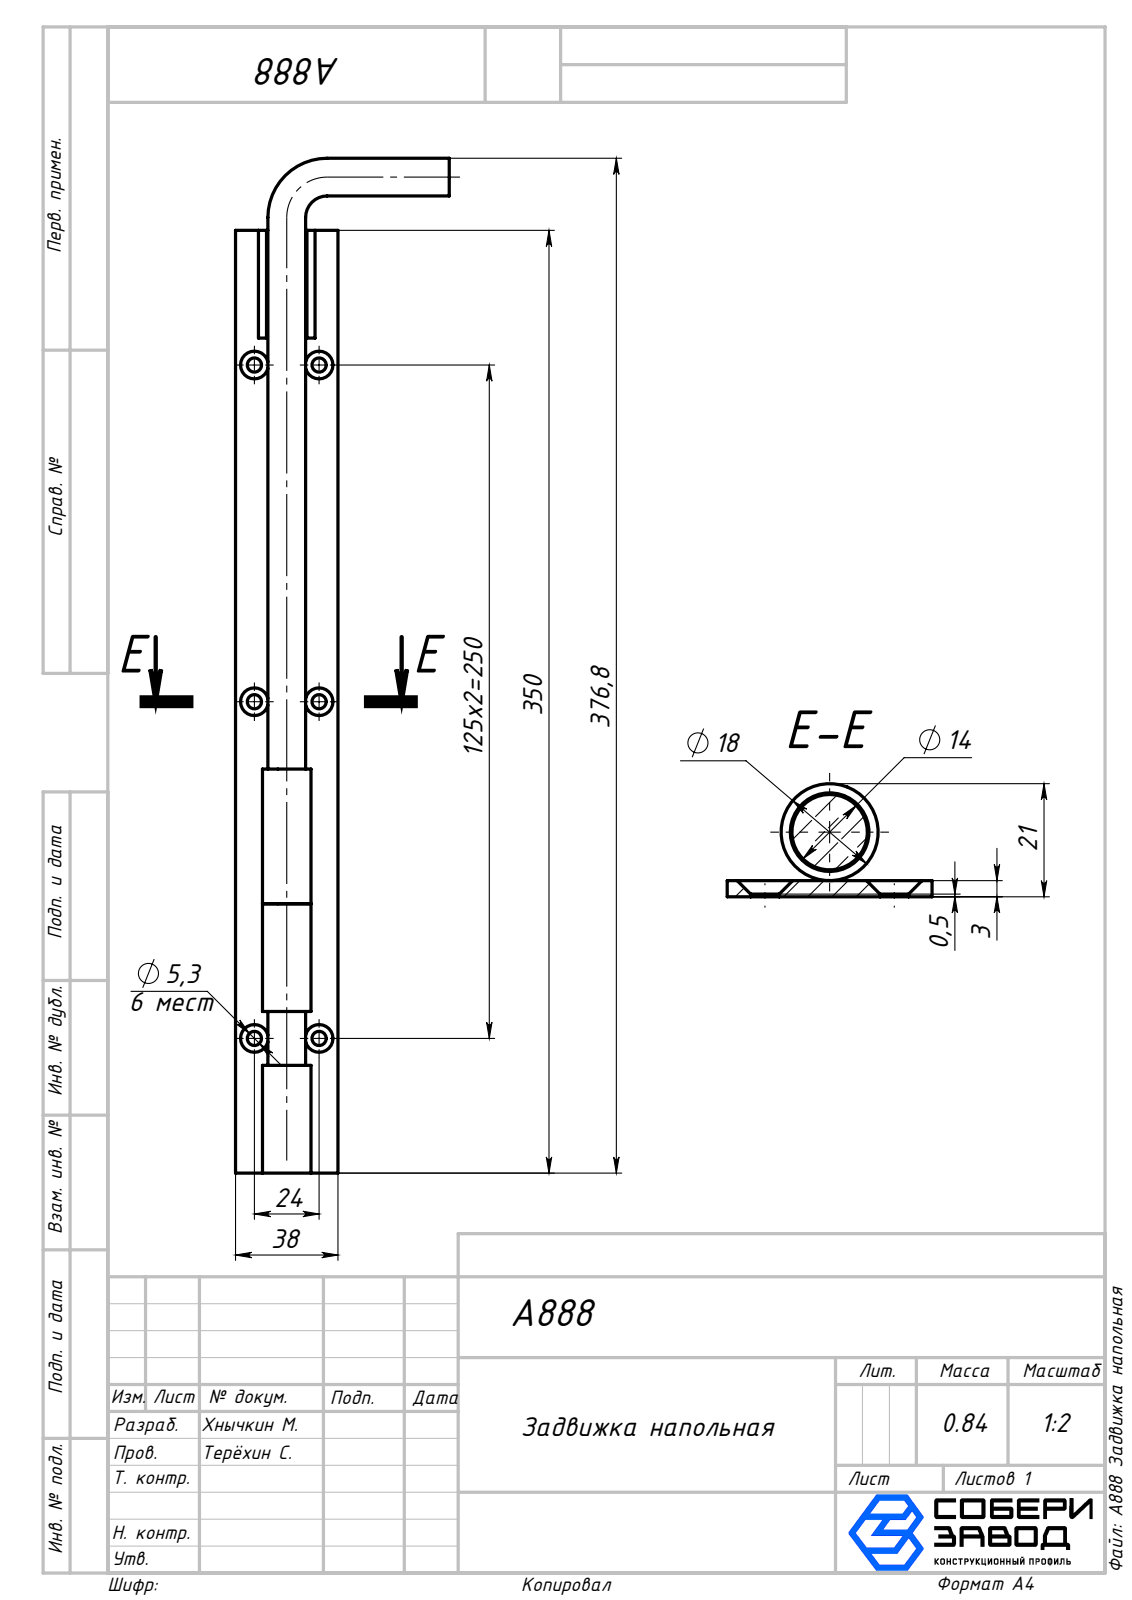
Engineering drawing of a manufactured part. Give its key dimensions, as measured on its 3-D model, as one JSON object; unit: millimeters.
{"part_name": "A888 Задвижка напольная; Г_00; Втулка_00; A888 Пластина_00", "step_written_by": "SolidWorks 2025 (AUTOMOTIVE_DESIGN)", "units": "millimeters", "bodies": {"solids": 5, "faces": 68, "planar": 24, "cylindrical": 30, "other": 14}, "overall_size": [376.77, 79.29, 23], "volume_mm3": 118746, "surface_area_mm2": 64495, "round_holes": [[5.3, 6], [14.6, 1]], "round_bosses_or_shafts": [[14, 2], [18, 1]], "partial_cylinders_radius": [[8.9, 1]], "face_to_face_distances": [3, 11.5, 26.5, 8.5, 29.5, 18, 38, 21, 15, 20], "hole_center_spacings": [125, 127.28, 24, 250, 251.15]}
